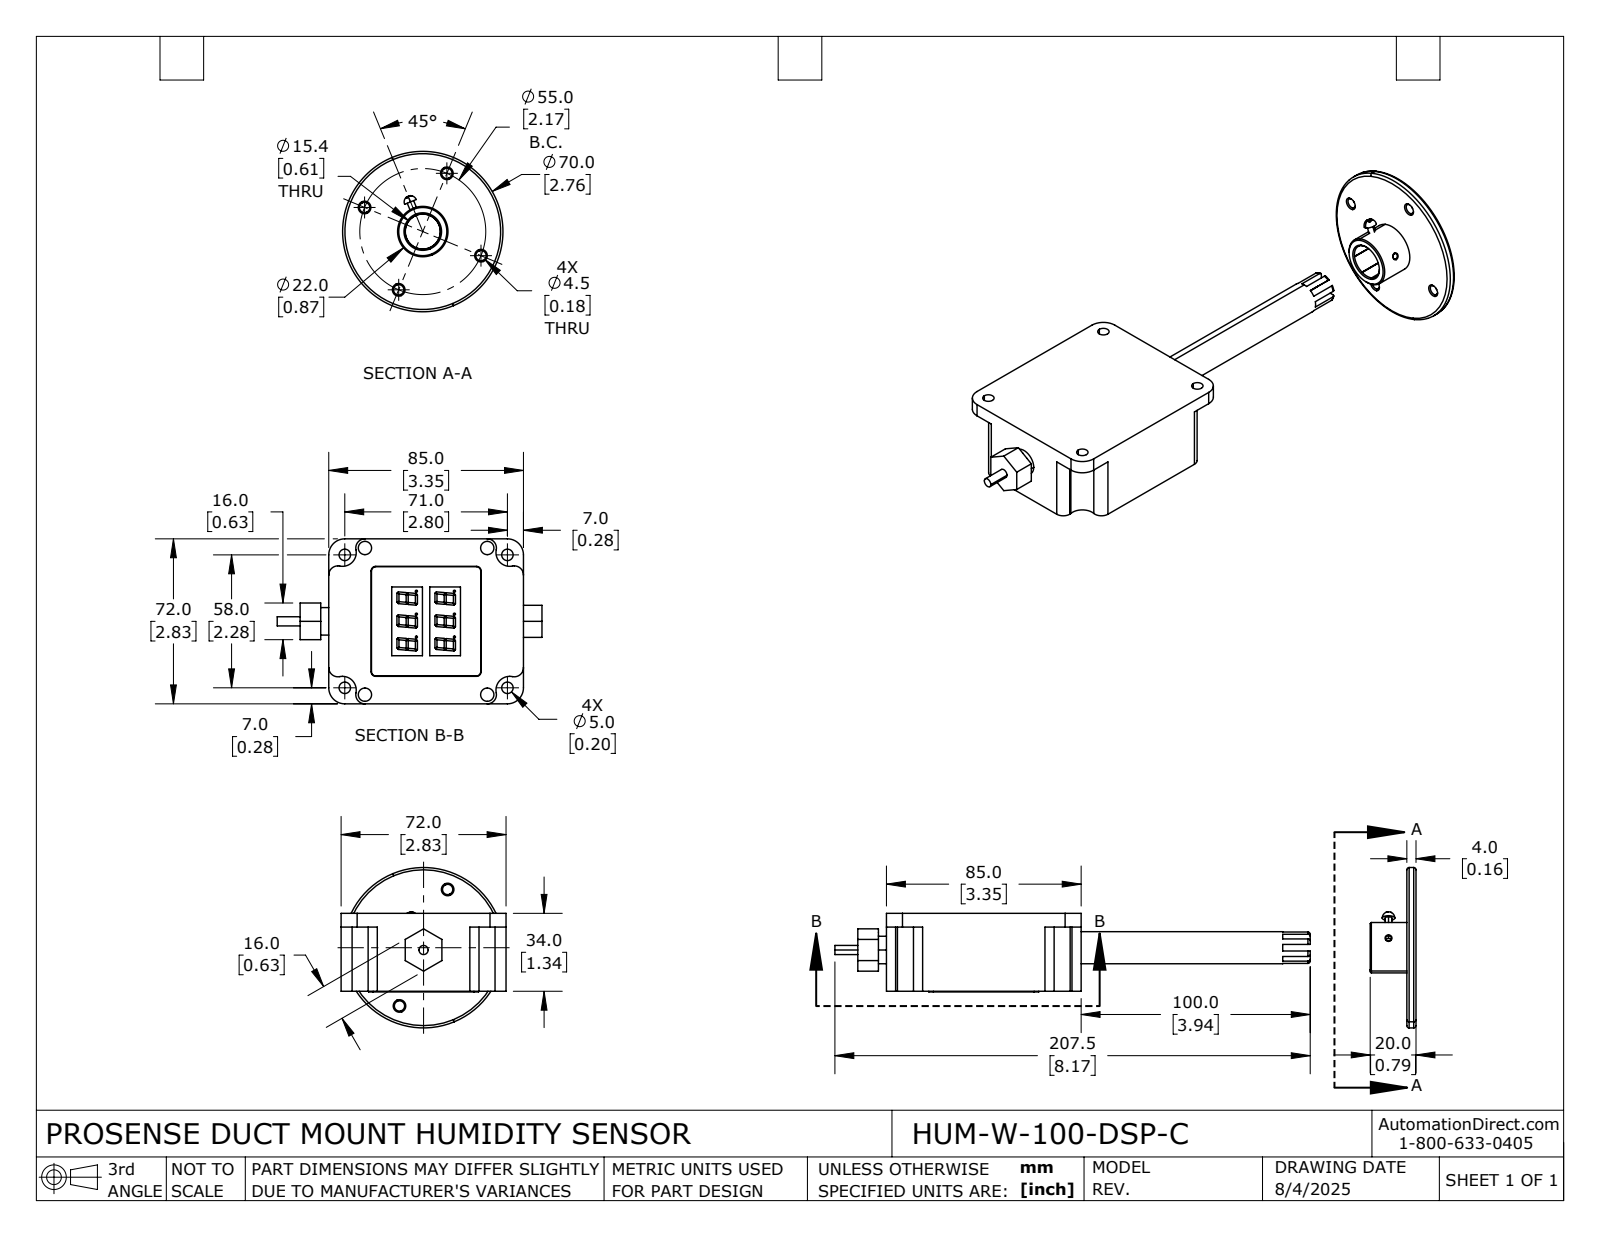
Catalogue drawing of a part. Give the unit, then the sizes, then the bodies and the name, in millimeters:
Units: millimetres
Overall size (bounding box): 253.7 × 72 × 70
Round holes (diameter × count): ⌀0.9 ×4, ⌀4.5 ×4, ⌀5 ×4, ⌀5.8 ×4, ⌀2.5 ×2
Round bosses / shafts (diameter × count): ⌀70 ×1, ⌀22 ×1, ⌀14 ×1, ⌀12 ×1, ⌀4 ×1, ⌀3 ×1
Partial cylindrical surfaces — rounded edges, fillets, slot ends (radius × count): R2 ×8, R4 ×8, R0.1 ×6, R6 ×4, R7 ×4, R0.8 ×1
Main face-to-face distances: 34, 4, 72, 231.2, 227.2, 146.2, 142.2, 85, 34.3, 28
Hole centre spacings: 9.3, 61.6, 62.3, 87.1, 10, 16.6, 19.4, 38.9
Volume: 225 300 mm³ · Surface area: 38 990 mm²
Bodies: 4 solids, 534 faces (385 planar, 95 cylindrical, 54 other)
Part name (STEP PRODUCT): HUM-W-100-DSP-C
STEP written by: SolidWorks 2024 (AUTOMOTIVE_DESIGN)
